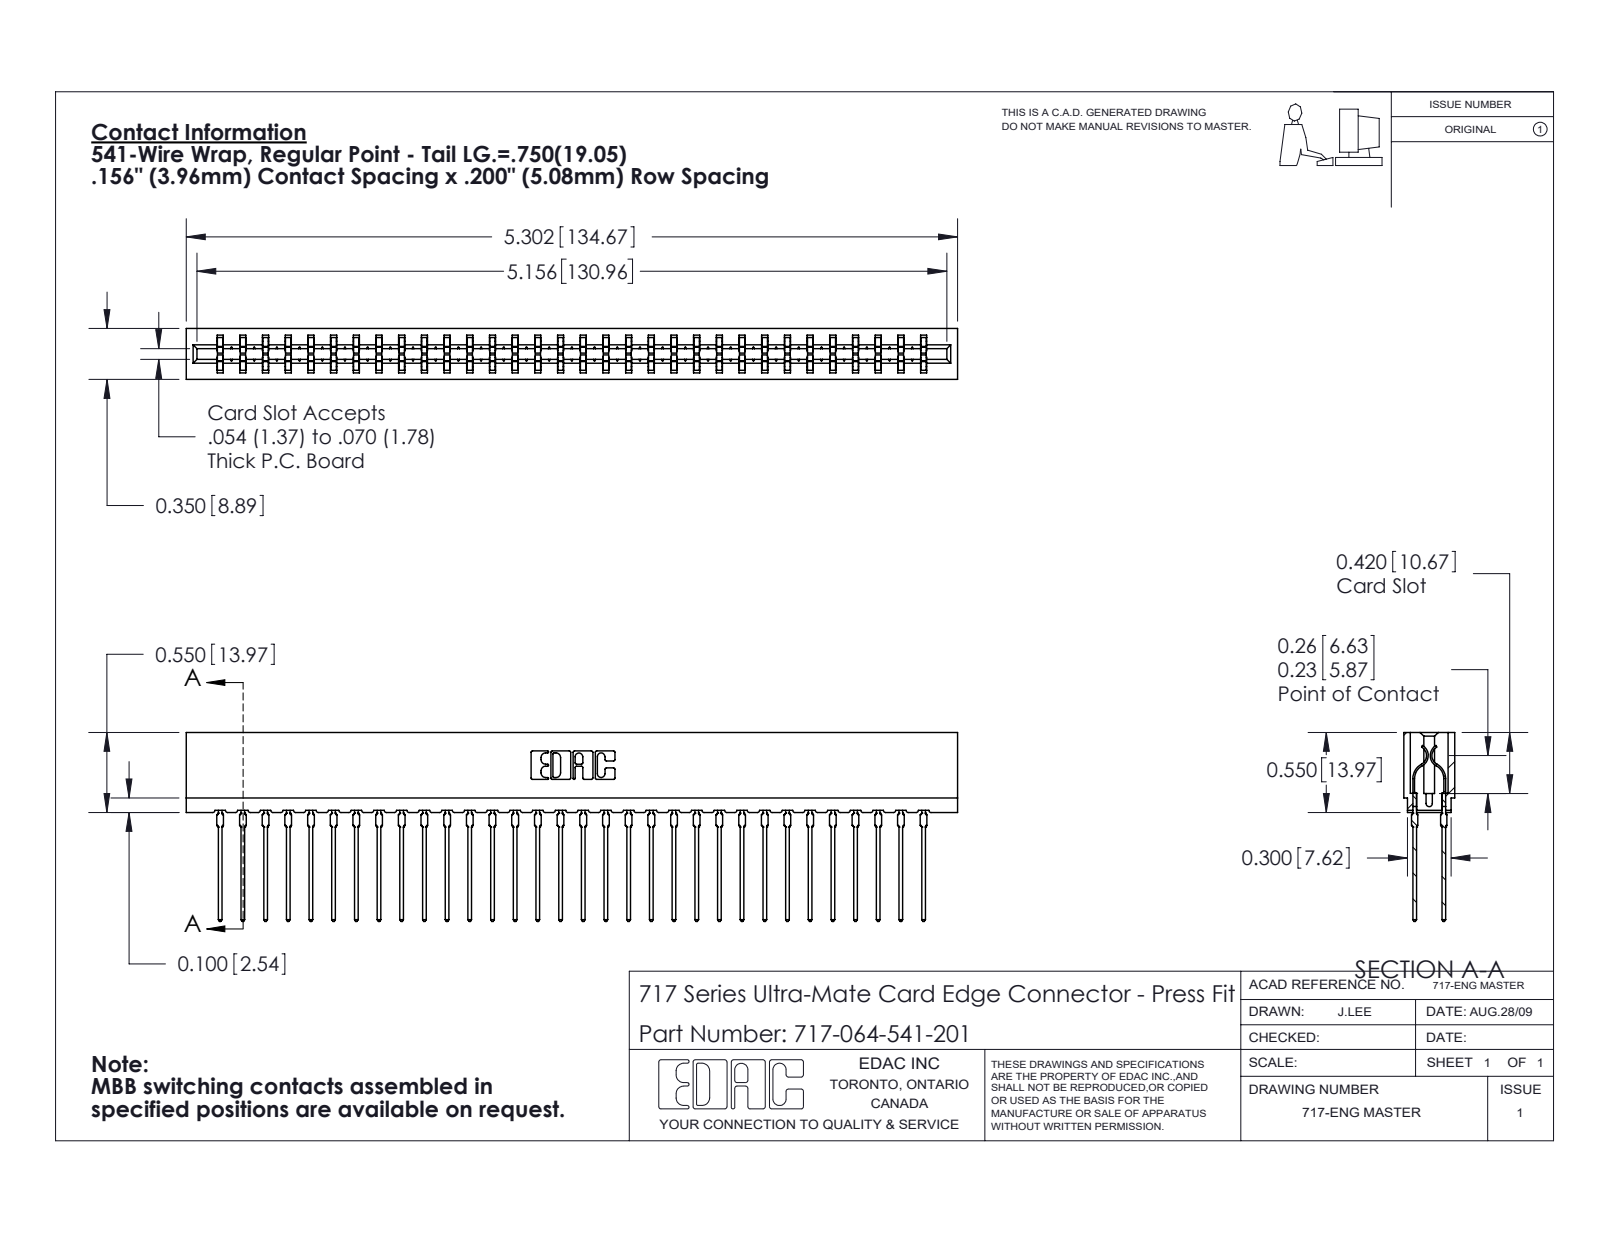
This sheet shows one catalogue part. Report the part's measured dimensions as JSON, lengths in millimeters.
{"part_name": "745-292-001_541; 717-064-541-201; 717 Part_Insulator Option - 06", "step_written_by": "SolidWorks 2020 (CONFIG_CONTROL_DESIGN)", "units": "millimeters", "bodies": {"solids": 65, "faces": 5854, "planar": 3030, "cylindrical": 1160, "other": 1664}, "overall_size": [134.7, 33, 8.9], "volume_mm3": 12000, "surface_area_mm2": 19680, "partial_cylinders_radius": [[0.5, 128], [0.4, 64], [0.3, 22], [0.1, 8], [0.3, 8], [0.2, 6], [0.8, 6], [0.7, 3]], "face_to_face_distances": [5.4, 3.5, 8.9, 1.6, 7.3, 1.9, 3.8, 2.2, 6.7, 0.6]}
